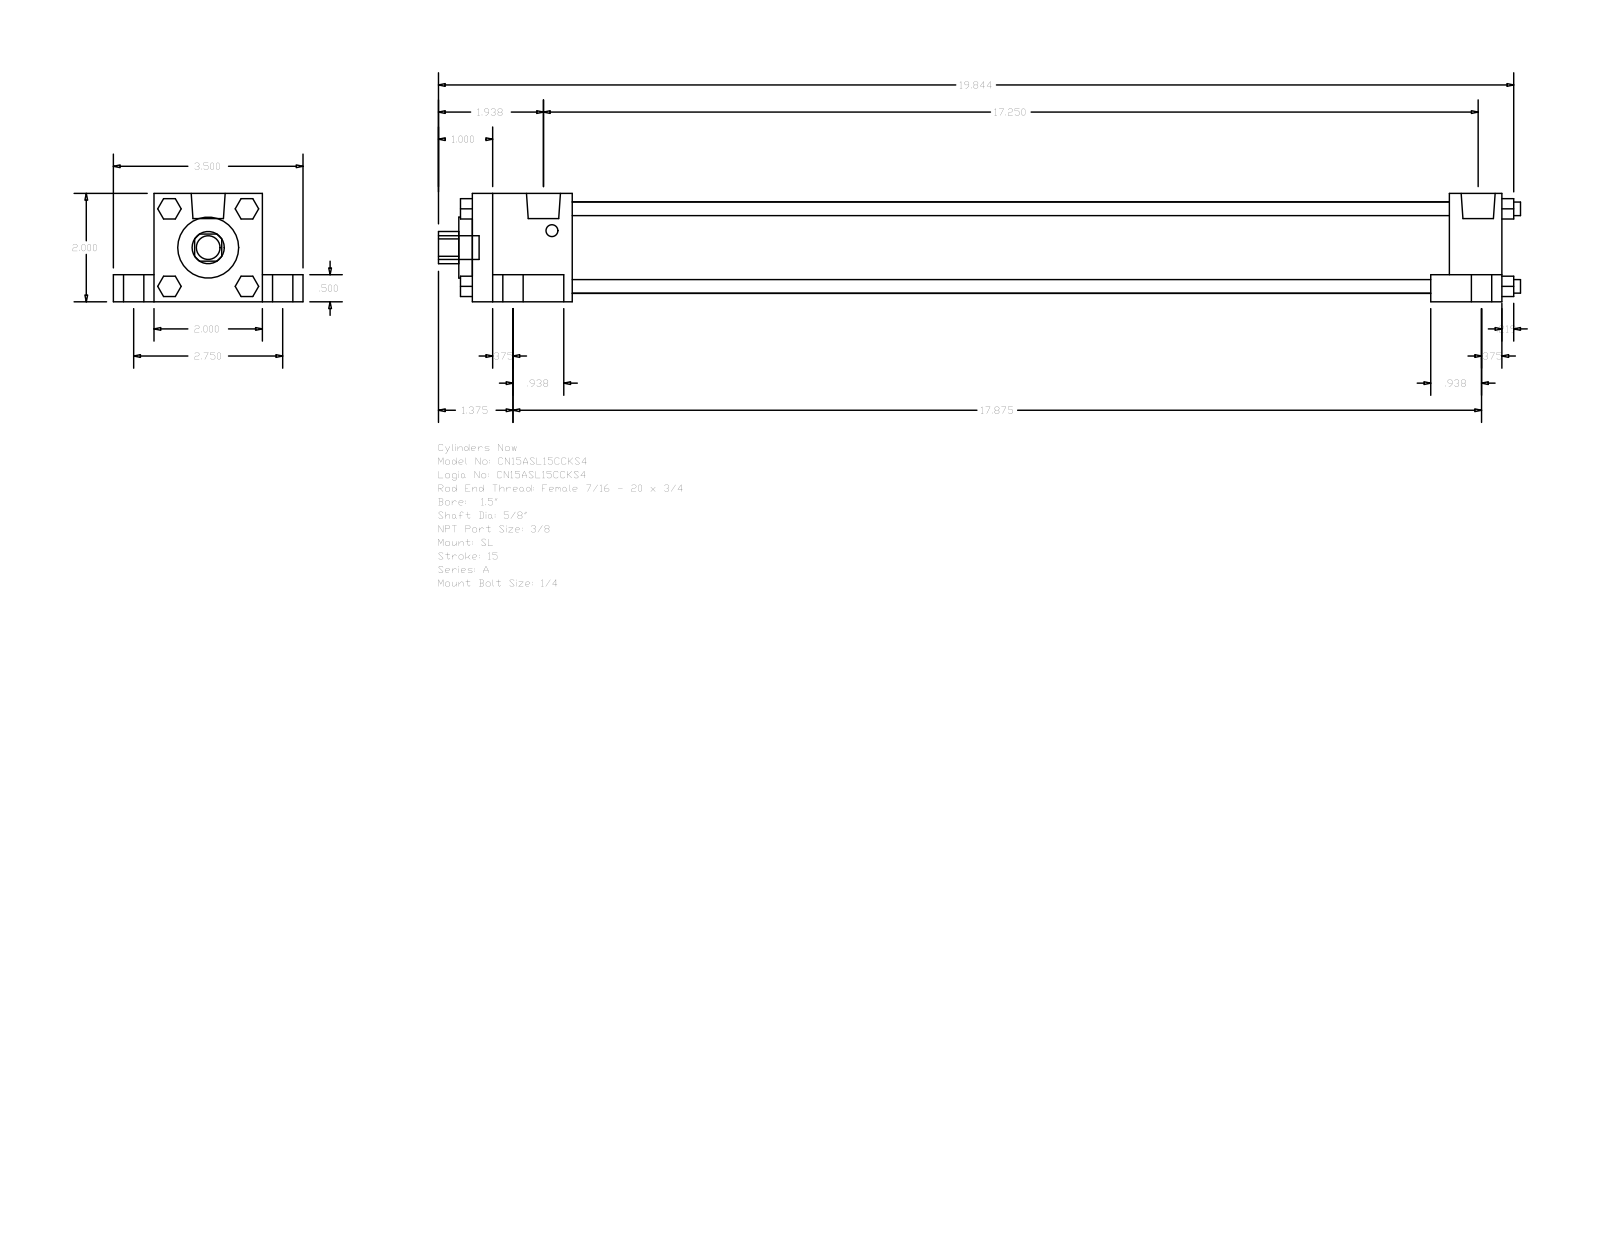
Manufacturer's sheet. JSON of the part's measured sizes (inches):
{"part_name": "A_SL__0150_0.625", "step_written_by": "GSSL Pune (CONFIG_CONTROL_DESIGN)", "units": "inches", "bodies": {"solids": 0, "faces": 148, "planar": 112, "cylindrical": 36, "other": 0}, "overall_size": [19.969, 3.5, 2], "round_holes": [[0.625, 1], [1.125, 1], [1.69, 1]], "round_bosses_or_shafts": [[0.625, 4], [0.375, 4], [0.25, 4], [0.219, 4], [0.627, 2], [0.437, 1]], "partial_cylinders_radius": [[0.297, 1]], "face_to_face_distances": [2, 0.75, 0.5, 1.5, 2.75, 19, 0.375, 1.313, 18.031, 0.969]}
